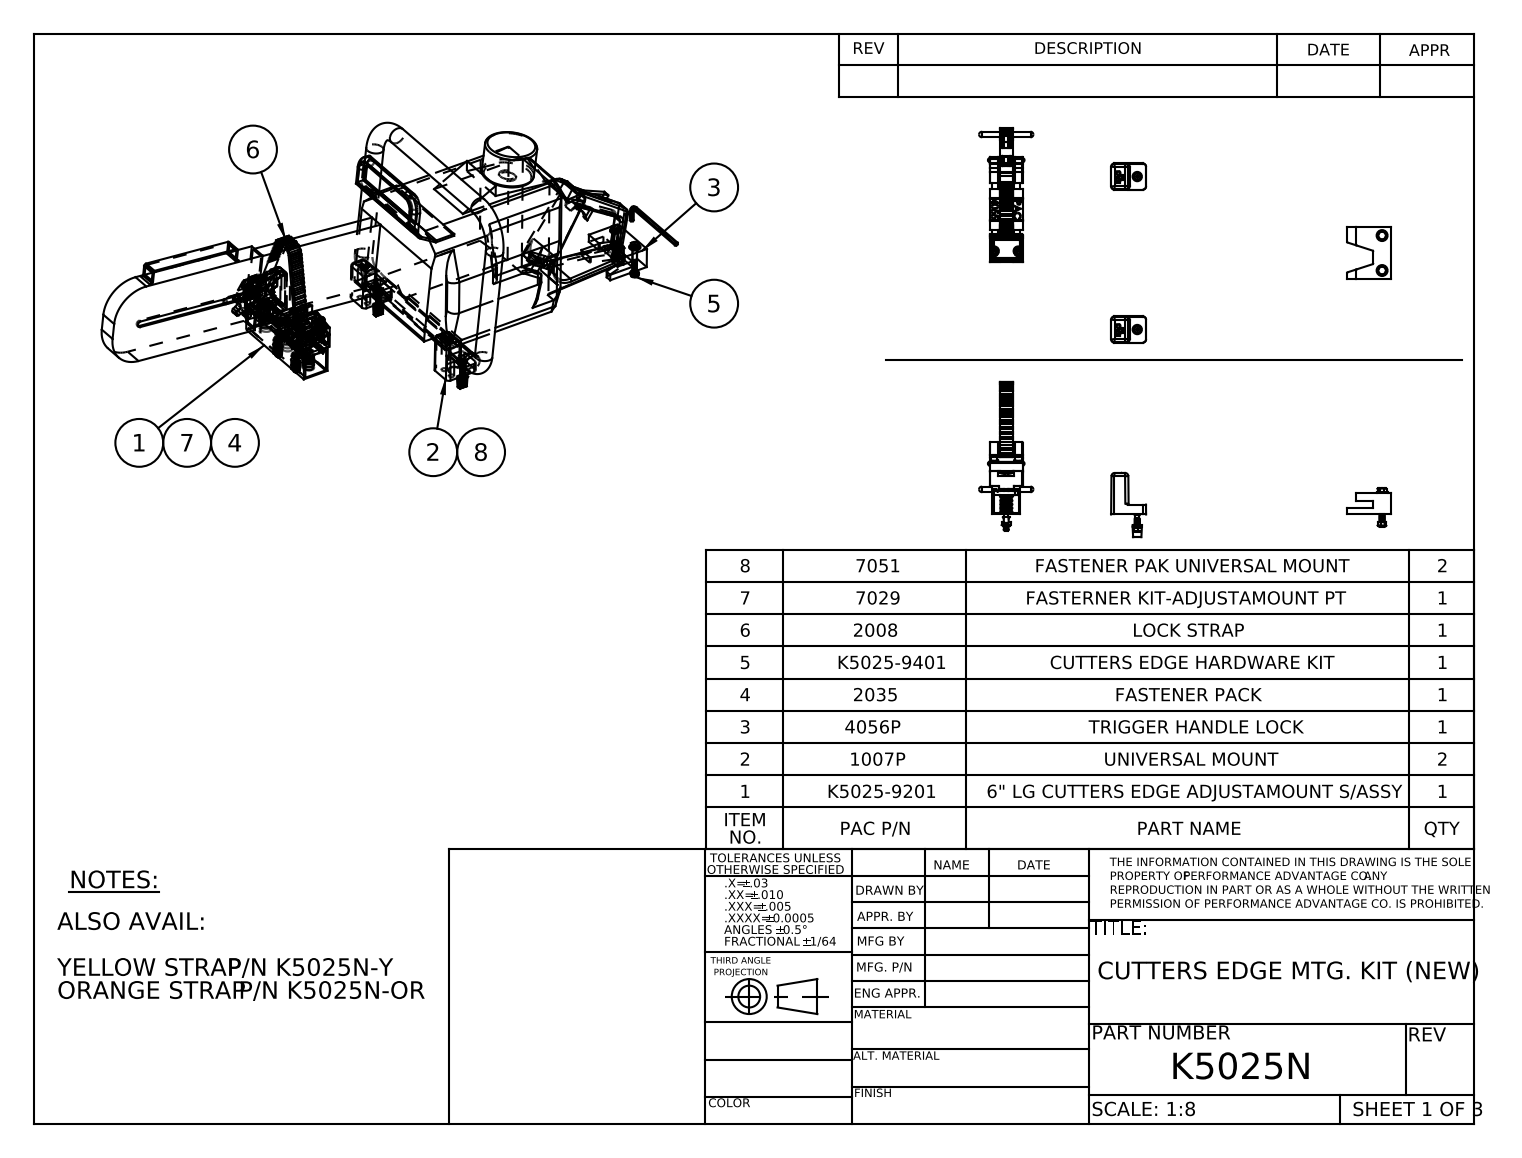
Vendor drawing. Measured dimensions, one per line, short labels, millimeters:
name: 1007; 4056N; 2018_compressed; 2032_8.75" APART (+8 more)
written by: SolidWorks 2010 (CONFIG_CONTROL_DESIGN)
unit: mm
bodies: 44 solids, 2120 faces (813 planar, 679 cylindrical, 628 other)
size: 872.7 × 353.1 × 318.6
volume: 11 770 000 mm³; area: 813 500 mm²
holes: 11× ⌀5.1, 6× ⌀6.4, 6× ⌀6.8, 6× ⌀6.8, 5× ⌀7.3, 2× ⌀6.6, 2× ⌀14.3, 1× ⌀7.4, 1× ⌀15.9, 1× ⌀16.3, 1× ⌀16.9
bosses: 8× ⌀6.4, 6× ⌀10.3, 5× ⌀25.4, 5× ⌀15.9, 5× ⌀9.5, 2× ⌀11.5, 1× ⌀76.2, 1× ⌀25.3
rounds: 71× R1.6, 43× R0.8, 42× R1.6, 41× R3.2, 30× R0.5, 23× R6.4, 18× R9.5, 13× R5.6
face distances: 25.4, 3.2, 23.8, 52.4, 28.6, 27, 49.2, 22.2, 1.6, 1.5
hole spacings: 23.8, 365.8, 380.9, 32.4, 33.4, 34.9, 47.6, 50.8
